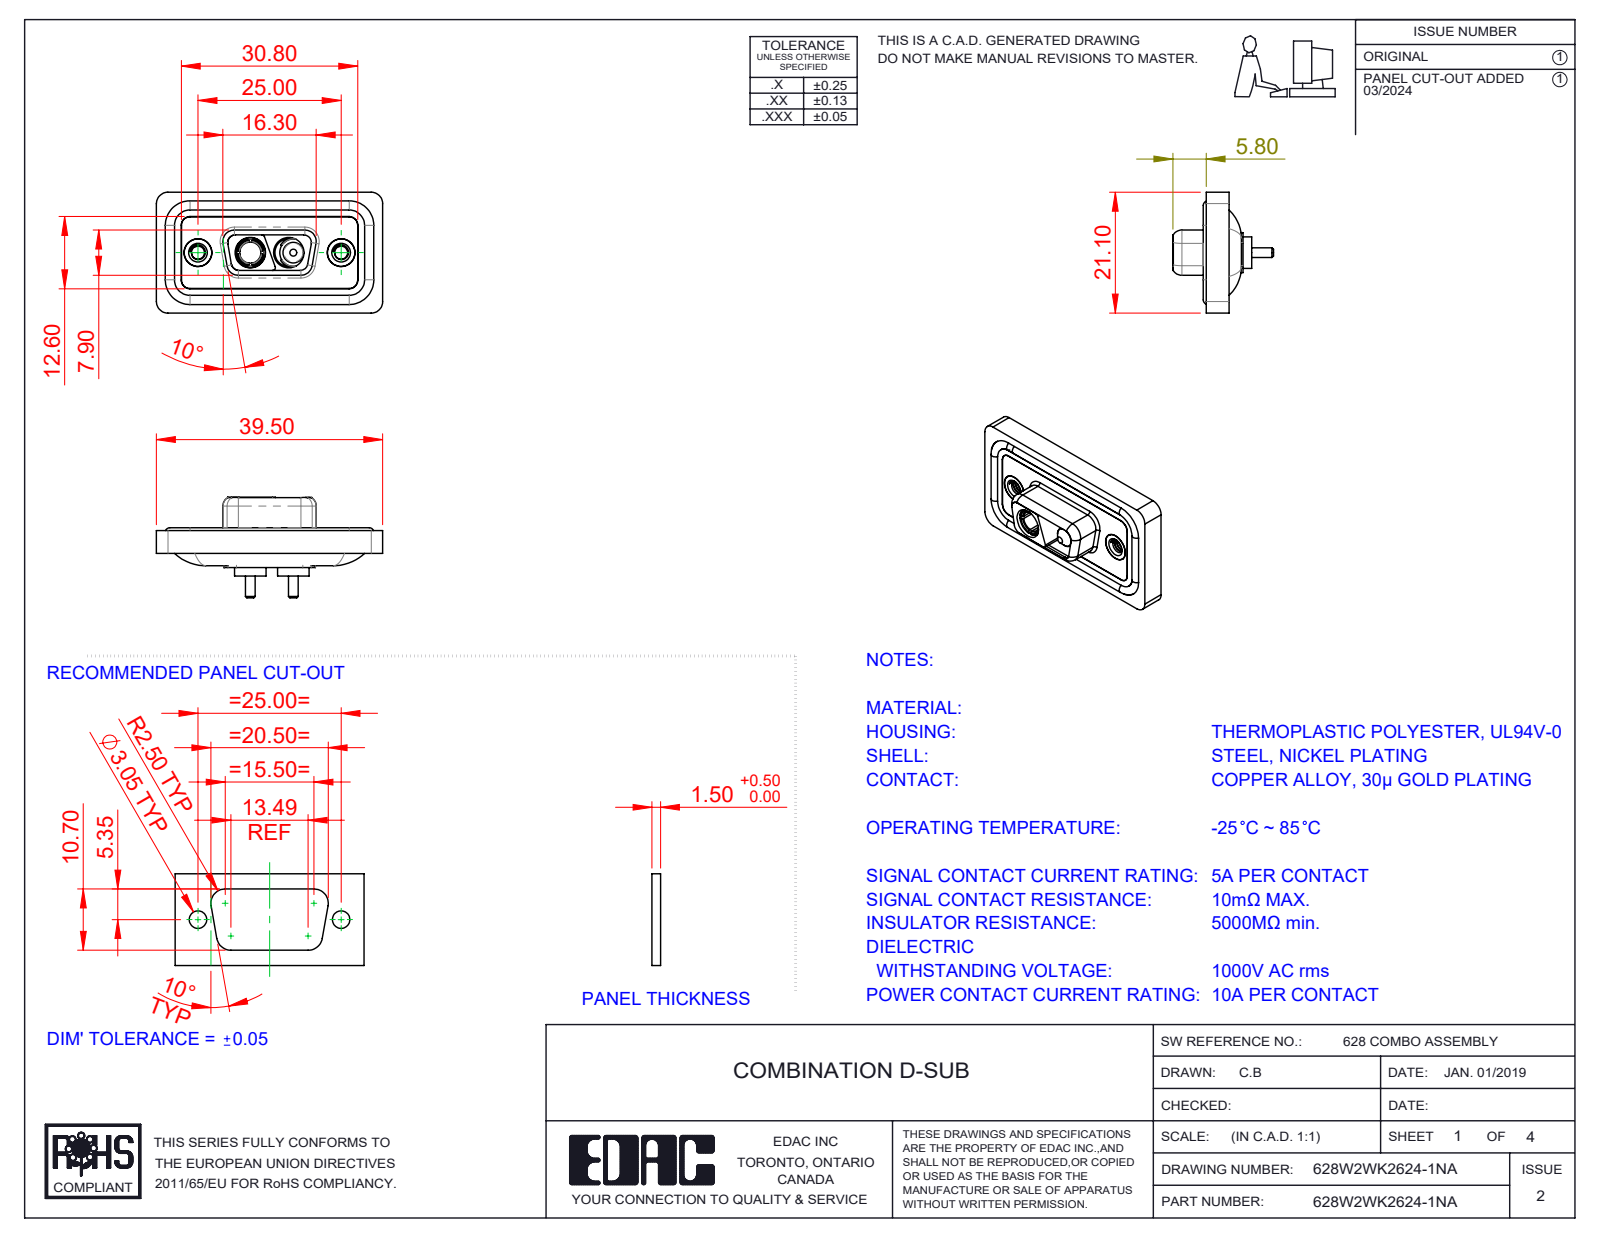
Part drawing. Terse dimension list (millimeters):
name: 628W2WK2624-1NA; 628Combo Shell Front_09 Contacts; Power Socket_10A S; 628Combo Housing_2WK2 (+4 more)
written by: SolidWorks 2023 (CONFIG_CONTROL_DESIGN)
unit: mm
bodies: 11 solids, 498 faces (144 planar, 233 cylindrical, 121 other)
size: 39.5 × 21.1 × 17.55
volume: 4 575 mm³; area: 7 316 mm²
holes: 4× ⌀4.85, 2× ⌀2.26, 2× ⌀4, 2× ⌀4.05, 2× ⌀5, 2× ⌀5.3, 1× ⌀3.7
bosses: 4× ⌀1.6, 2× ⌀5.5, 2× ⌀5.2, 2× ⌀4.95, 2× ⌀4.8, 2× ⌀4.75, 2× ⌀3.75, 2× ⌀1.7
rounds: 22× R1.5, 18× R2, 8× R1.35, 8× R1.6, 6× R0.5, 4× R0.25, 4× R0.6, 4× R0.65
face distances: 0.4, 1.1, 2.9, 1.6, 0.5, 1.8, 5.65, 1.5, 5.35, 3.1
hole spacings: 9.14, 15.86, 6.72, 25
